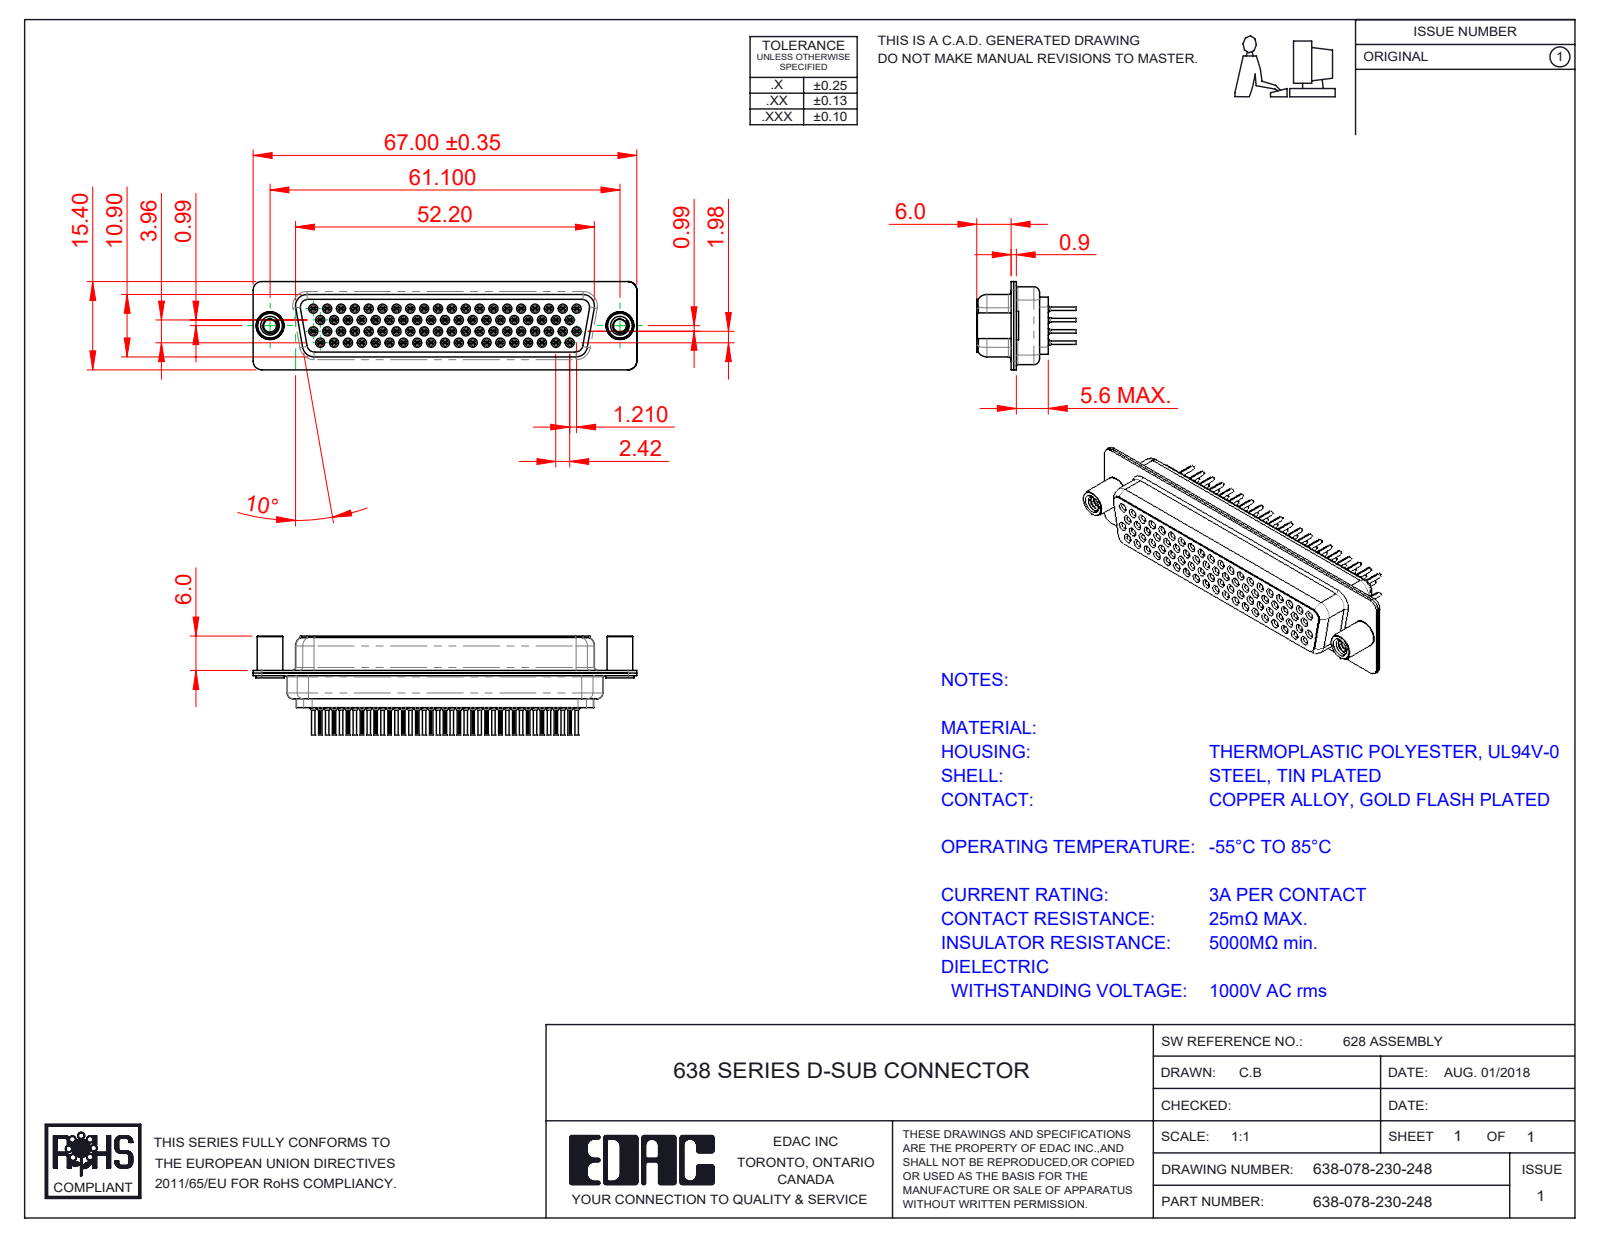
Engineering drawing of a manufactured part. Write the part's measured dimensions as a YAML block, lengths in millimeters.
part_name: "638 Housing_78 Contacts; 638-078-230-248; 638 Contact Row 3_30; 638 4-40 Threaded Standoff (+5 more)"
step_written_by: "SolidWorks 2020 (CONFIG_CONTROL_DESIGN)"
units: millimeters
bodies: {solids: 83, faces: 10219, planar: 2487, cylindrical: 2739, other: 4993}
overall_size: [67, 17.3, 15.4]
volume: 5938
surface_area: 20717
round_holes:
  - {diameter: 0.2, count: 78}
  - {diameter: 0.8, count: 78}
  - {diameter: 1, count: 78}
  - {diameter: 1.1, count: 78}
  - {diameter: 1.6, count: 78}
  - {diameter: 1.7, count: 78}
  - {diameter: 1.8, count: 78}
  - {diameter: 2.26, count: 2}
  - {diameter: 4, count: 2}
  - {diameter: 4.05, count: 2}
  - {diameter: 4.85, count: 2}
round_bosses_or_shafts:
  - {diameter: 2, count: 78}
  - {diameter: 1.5, count: 78}
  - {diameter: 1.2, count: 78}
  - {diameter: 0.6, count: 78}
  - {diameter: 5, count: 2}
  - {diameter: 4.95, count: 2}
  - {diameter: 4.8, count: 2}
  - {diameter: 4.5, count: 2}
partial_cylinders:
  - {radius: 0.1, count: 156}
  - {radius: 0.28, count: 39}
  - {radius: 1.5, count: 16}
  - {radius: 2, count: 12}
  - {radius: 1.55, count: 8}
  - {radius: 0.25, count: 4}
  - {radius: 0.5, count: 4}
  - {radius: 0.55, count: 4}
face_to_face_distances: [0.45, 0.4, 0.9, 1.35, 9.6, 1.8, 11.8, 11.4, 2.2, 0.85]
hole_center_spacings: [2.42, 4.84, 7.26, 9.68, 6.06, 12.1, 6.96, 8.48]
